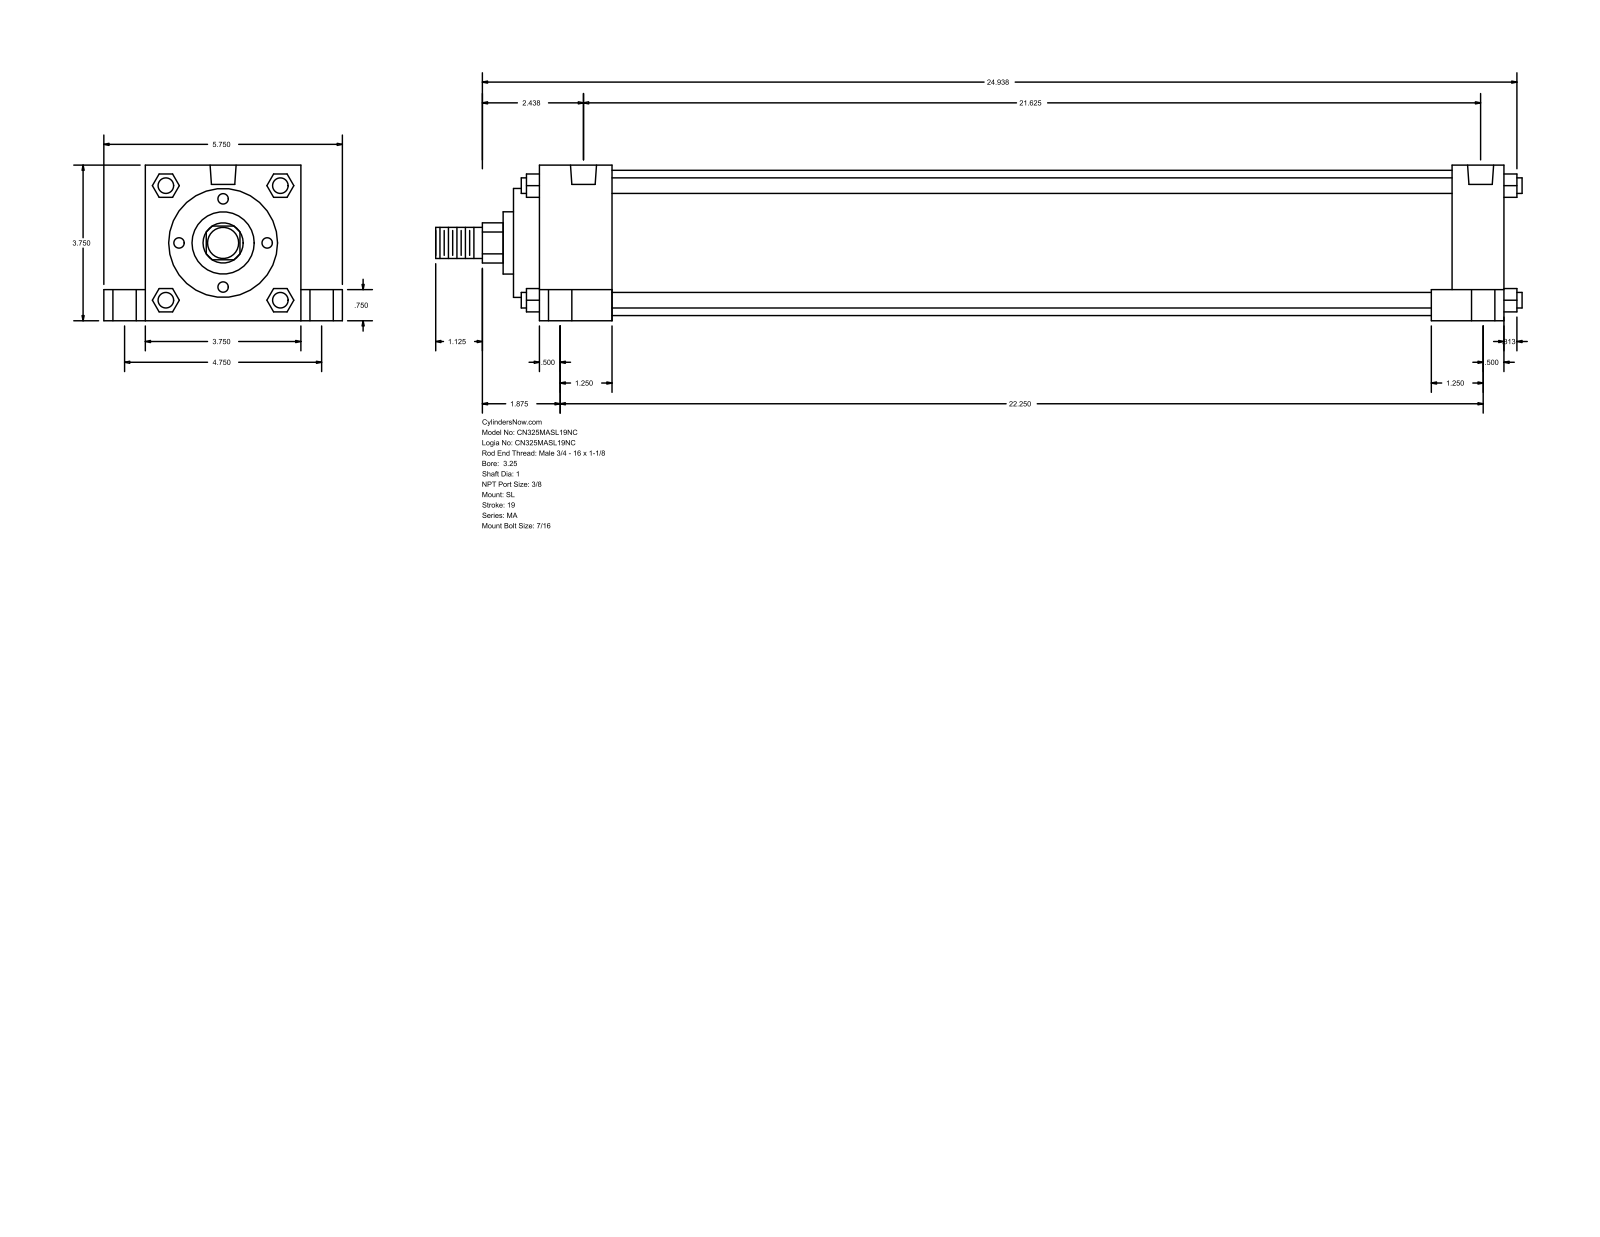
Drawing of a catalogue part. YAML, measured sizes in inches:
part_name: "MA_SL__0325_1"
step_written_by: "GSSL Pune (CONFIG_CONTROL_DESIGN)"
units: inches
bodies: {solids: 0, faces: 150, planar: 113, cylindrical: 37, other: 0}
overall_size: [26.187, 5.75, 3.75]
round_holes:
  - {diameter: 0.437, count: 4}
  - {diameter: 0.563, count: 4}
  - {diameter: 0.813, count: 4}
  - {diameter: 0.627, count: 2}
round_bosses_or_shafts:
  - {diameter: 0.375, count: 4}
  - {diameter: 3.5, count: 1}
  - {diameter: 2.625, count: 1}
  - {diameter: 1.5, count: 1}
  - {diameter: 1, count: 1}
  - {diameter: 0.75, count: 1}
partial_cylinders:
  - {radius: 0.484, count: 1}
face_to_face_distances: [3.75, 23.25, 20.25, 0.625, 1, 4.75, 0.75, 22, 1.25, 1.75]
hole_center_spacings: [2.376, 2.388, 2.441, 2.491, 4.75, 21.25, 21.631, 21.817]
